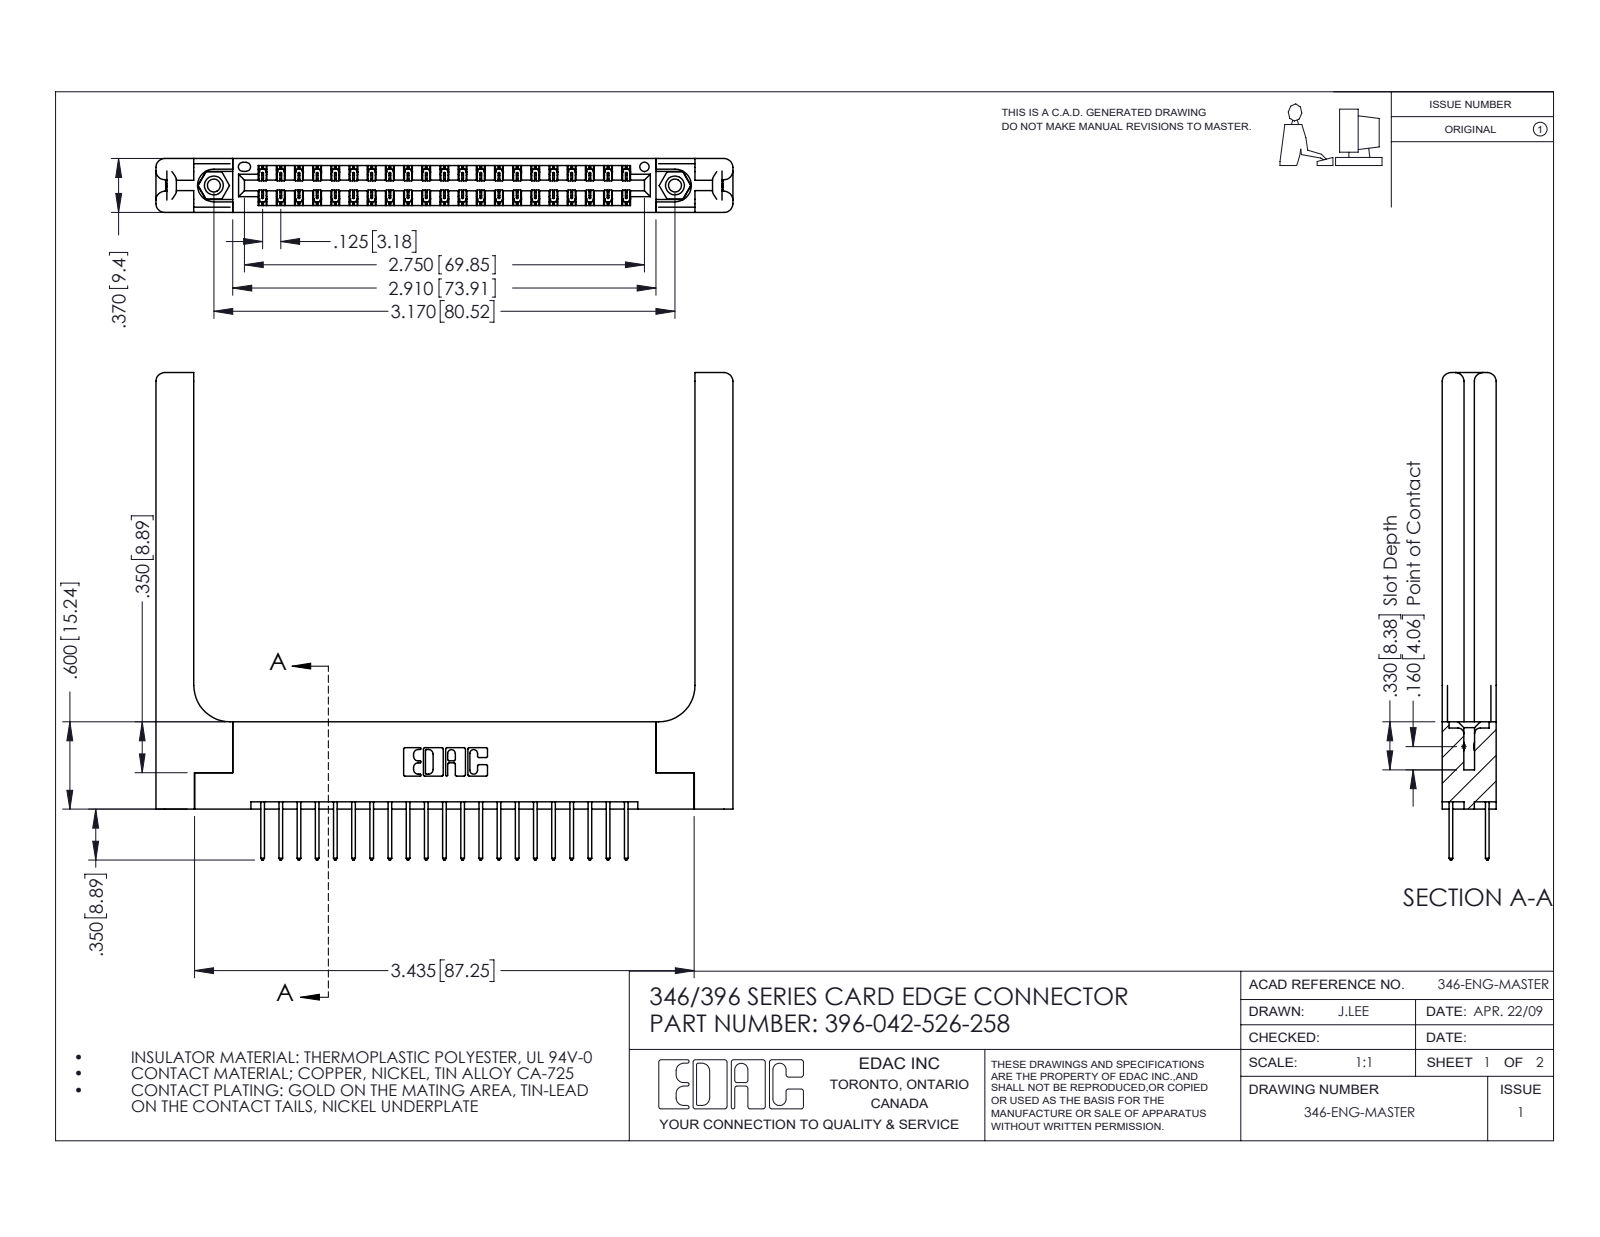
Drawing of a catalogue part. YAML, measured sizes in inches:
part_name: "346-220-058_345-220-058; 346 Part_Flush Mounting Lugs - 0.156 Dia-TH; 345-250-001_345-250-001-102; 345-292-001_345-293-126 (+1 more)"
step_written_by: "SolidWorks 2016 (CONFIG_CONTROL_DESIGN)"
units: inches
bodies: {solids: 47, faces: 2562, planar: 1694, cylindrical: 808, other: 60}
overall_size: [3.966, 3.35, 0.37]
volume: 1.051
surface_area: 28.4
round_holes:
  - {diameter: 0.089, count: 2}
  - {diameter: 0.125, count: 2}
  - {diameter: 0.156, count: 2}
  - {diameter: 0.064, count: 1}
round_bosses_or_shafts:
  - {diameter: 0.155, count: 2}
partial_cylinders:
  - {radius: 0.006, count: 63}
  - {radius: 0.01, count: 42}
  - {radius: 0.01, count: 22}
  - {radius: 0.06, count: 16}
  - {radius: 0.007, count: 6}
  - {radius: 0.031, count: 6}
  - {radius: 0.026, count: 3}
  - {radius: 0.014, count: 2}
face_to_face_distances: [0.37, 0.072, 0.048, 0.322, 0.148, 0.15, 0.25, 0.025, 0.298, 0.275]
hole_center_spacings: [0.246, 2.963, 3.17]
